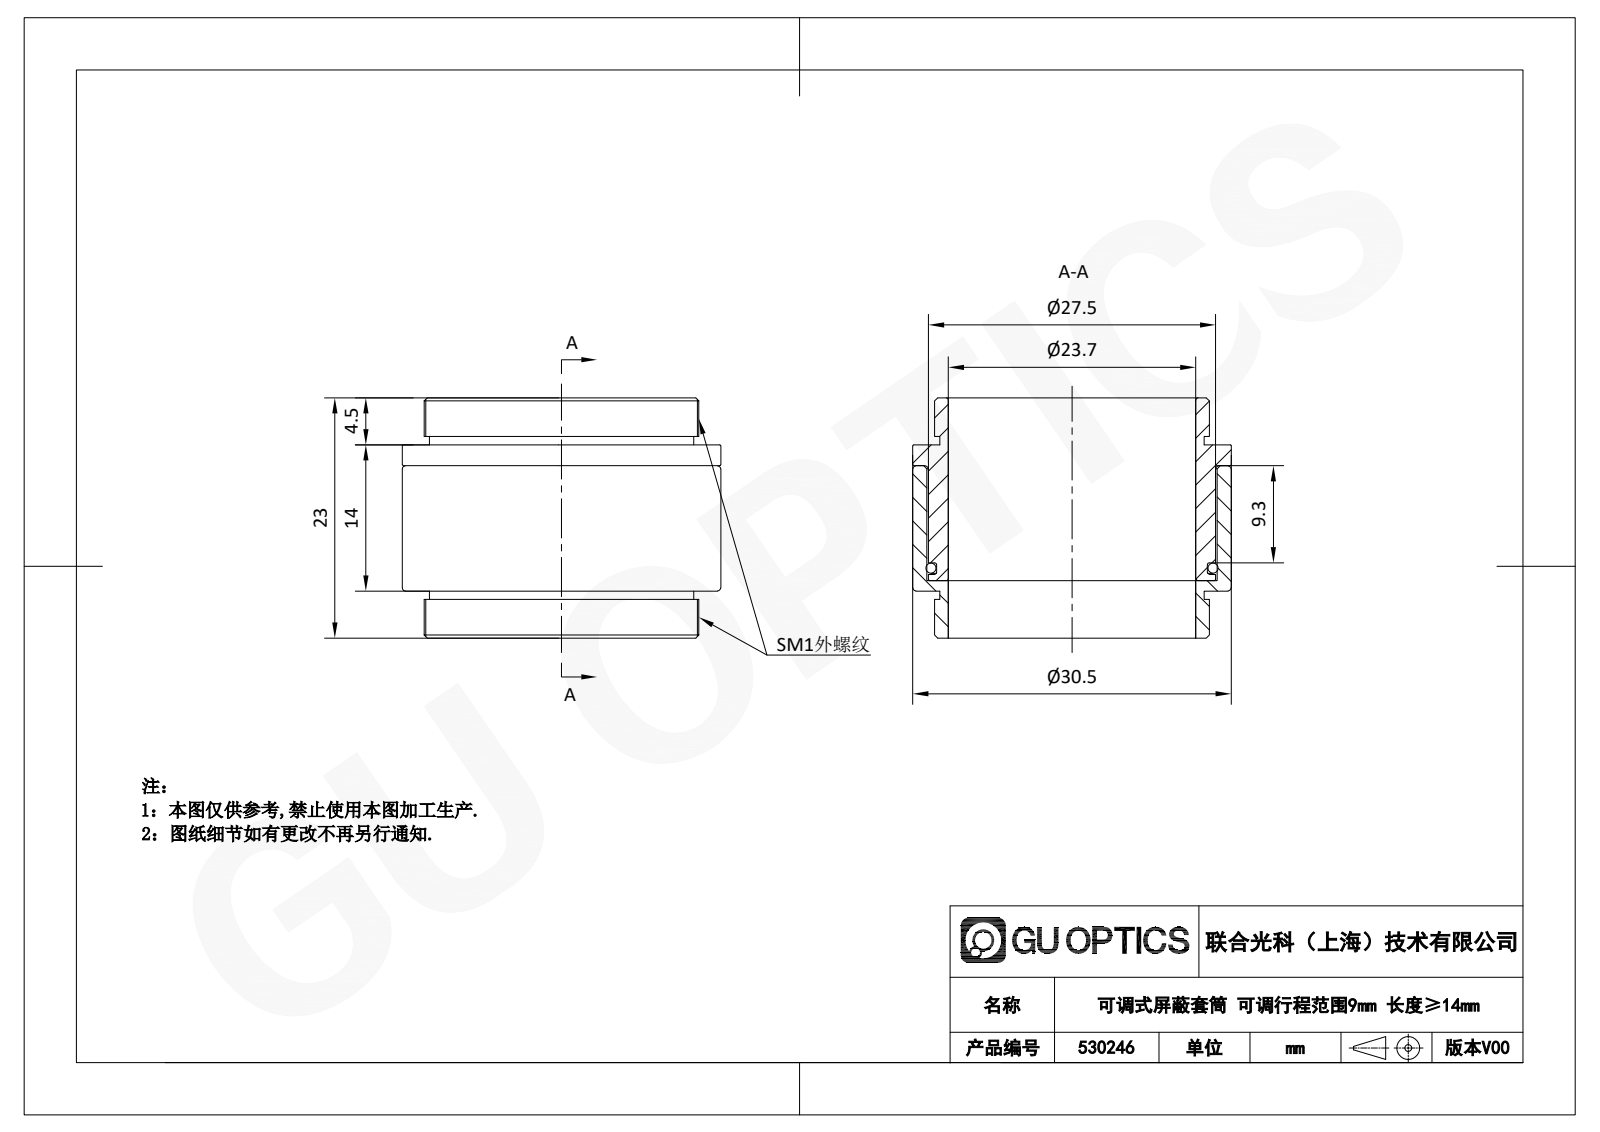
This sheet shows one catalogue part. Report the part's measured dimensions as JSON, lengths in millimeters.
{"part_name": "530246; 3.03.31.15.205_SM1屏蔽套筒组件2_SM1-SC14-2_ZA; 3.03.31.15.204_SM1屏蔽套筒组件1_SM1-SC14-1_ZA; 24-26_O形圈", "step_written_by": "SolidWorks 2020 (CONFIG_CONTROL_DESIGN)", "units": "millimeters", "bodies": {"solids": 3, "faces": 38, "planar": 12, "cylindrical": 12, "other": 14}, "overall_size": [30.5, 30.5, 23], "volume_mm3": 4739, "surface_area_mm2": 7300, "round_holes": [[23.7, 1], [27.8, 1]], "round_bosses_or_shafts": [[30.5, 1], [27.5, 1], [26.3, 1], [25.9, 1], [25.3, 1]], "face_to_face_distances": [13, 14, 1, 2, 11, 12, 4.5, 18.5, 3.7, 19.3]}
